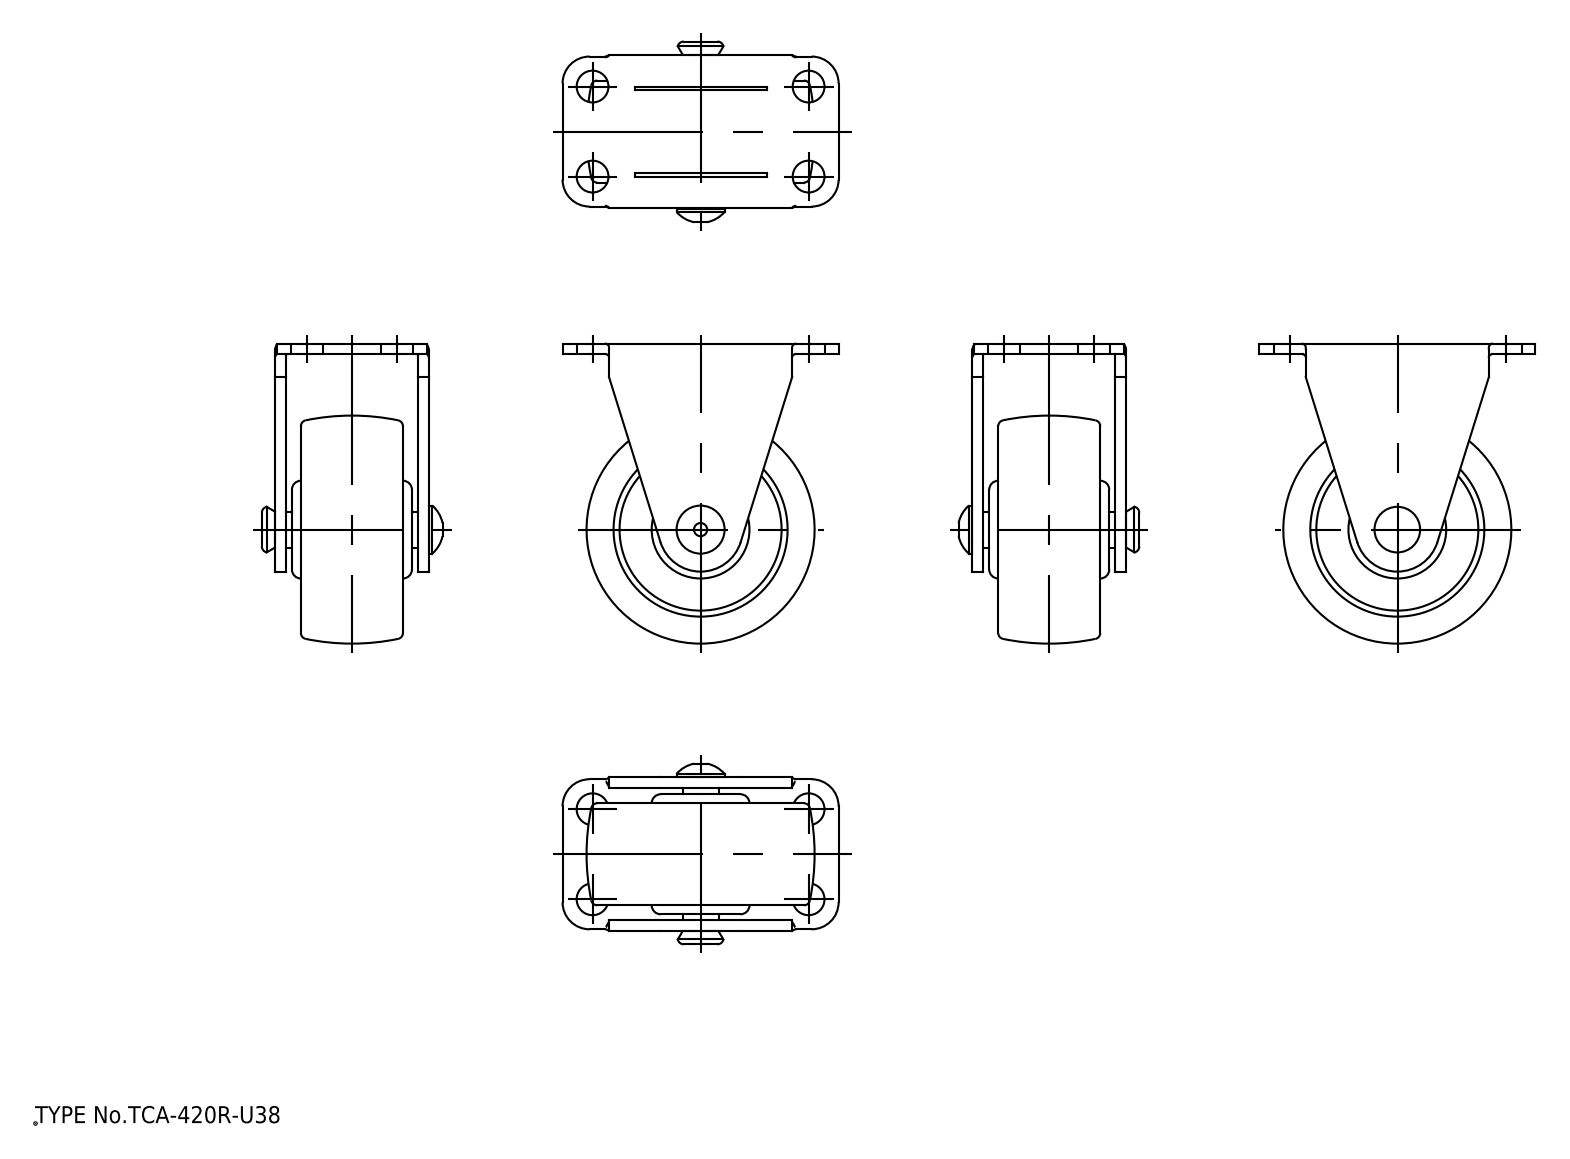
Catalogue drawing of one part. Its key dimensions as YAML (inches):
part_name: "wheel; axle"
step_written_by: "spGate 19.8.4 (****-****-****-****) (AUTOMOTIVE_DESIGN)"
units: inches
bodies: {solids: 3, faces: 113, planar: 39, cylindrical: 36, other: 38}
overall_size: [1.969, 1.811, 1.185]
volume: 1.415
surface_area: 16.91
round_holes:
  - {diameter: 0.209, count: 4}
  - {diameter: 0.236, count: 1}
round_bosses_or_shafts:
  - {diameter: 0.641, count: 1}
  - {diameter: 0.315, count: 1}
partial_cylinders:
  - {radius: 0.039, count: 4}
  - {radius: 0.177, count: 4}
  - {radius: 0.02, count: 2}
  - {radius: 0.276, count: 1}
face_to_face_distances: [0.071, 0.937, 0.728, 0.098, 0.039, 0.209, 0.799, 0.138, 0.866, 1.008]
hole_center_spacings: [0.591, 1.417, 1.535]
